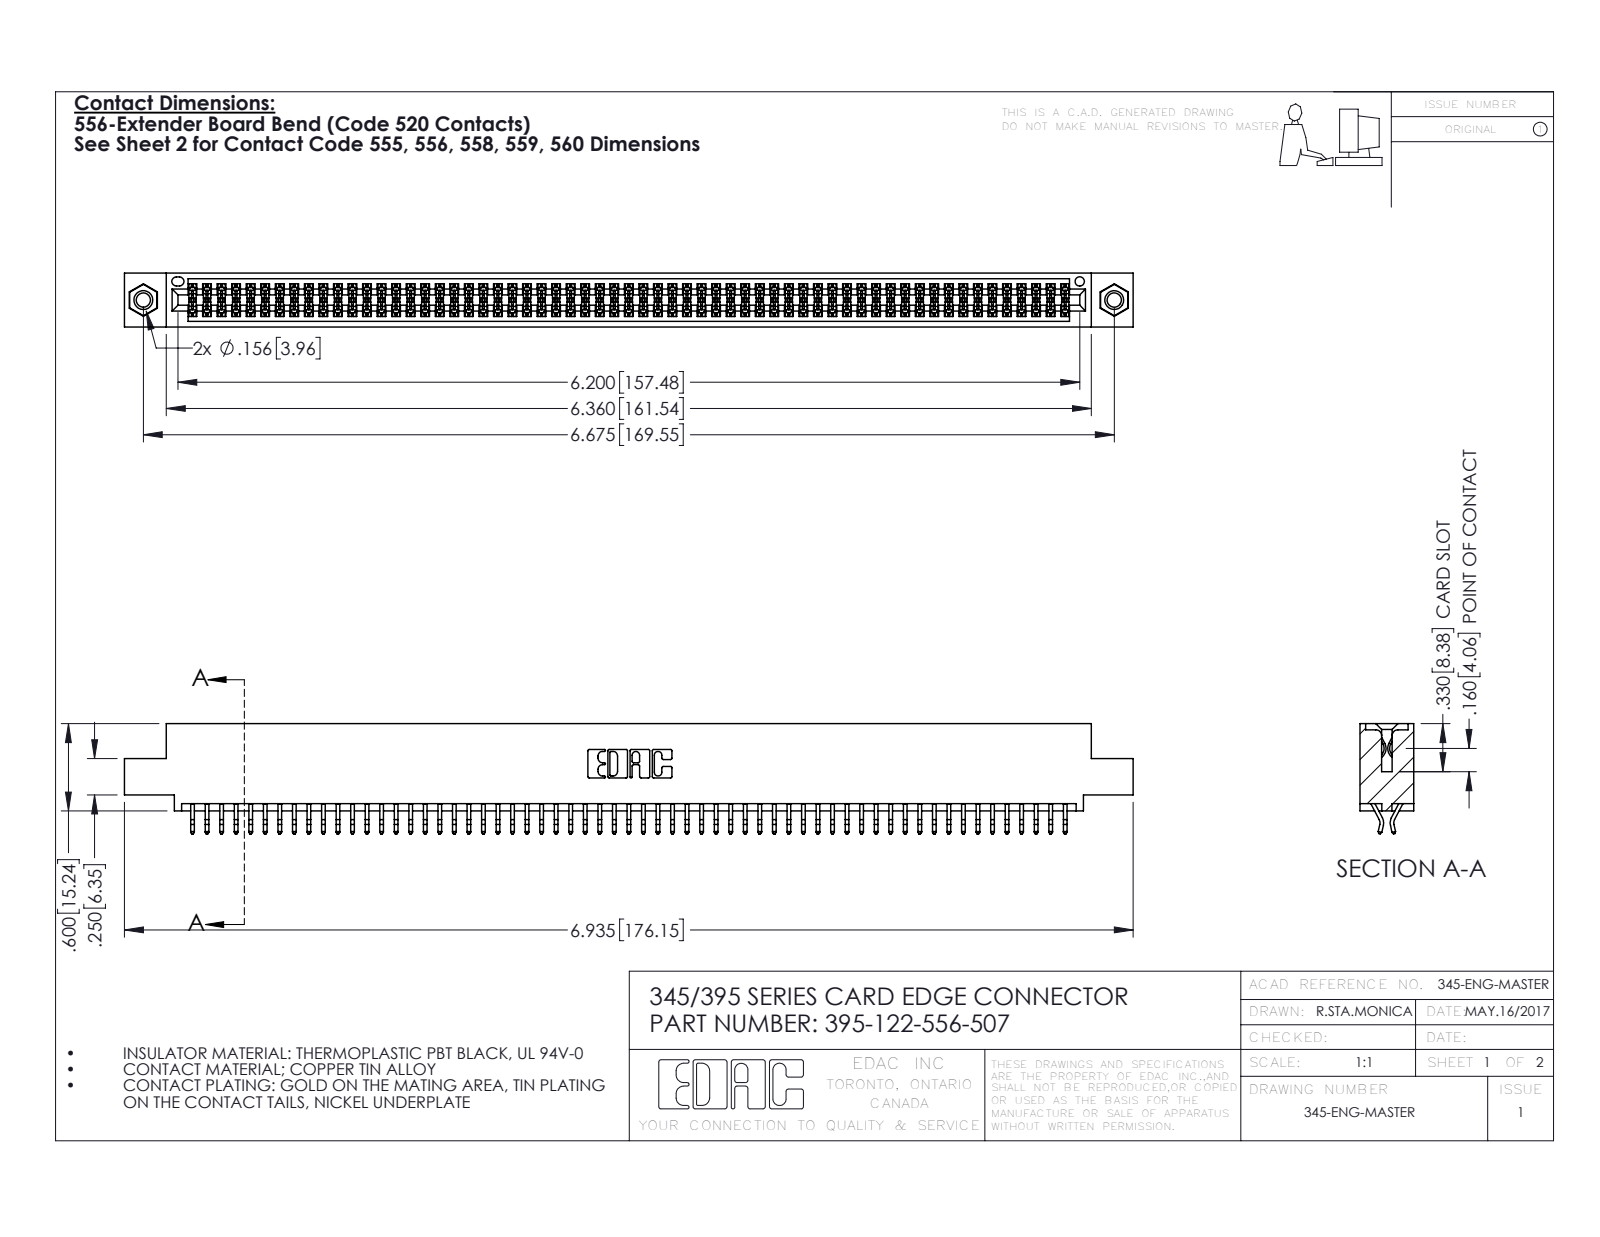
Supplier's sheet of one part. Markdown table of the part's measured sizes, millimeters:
| quantity | value |
| --- | --- |
| part name | 345-292-001_556 Tail; 345-250-001_345-250-005-103; 345 Part_0.110 Offset - 0.156 Dia-TI; 395-122-556-507 |
| STEP written by | SolidWorks 2016 (CONFIG_CONTROL_DESIGN) |
| units | millimeters |
| bodies | 125 solids, 7022 faces (4630 planar, 2376 cylindrical, 16 other) |
| overall size | 176.1 × 19.2 × 9.4 |
| volume | 17 190 mm³ |
| surface area | 25 800 mm² |
| round holes (diameter × count) | 2.5 × 2, 3.2 × 2, 4 × 2, 1.6 × 1 |
| round bosses / shafts (diameter × count) | 3.9 × 2 |
| partial cylindrical surfaces (radius × count) | 0.2 × 183, 0.3 × 22, 0.2 × 6, 0.8 × 6, 0.7 × 3, 0.3 × 2, 0.4 × 2, 0.5 × 2 |
| main face-to-face distances | 1.8, 7.6, 9.4, 5.1, 0.6, 2.5, 6.9, 5.7, 4.4, 3.8 |
| hole center spacings | 6.9, 163.6, 169.5 |
